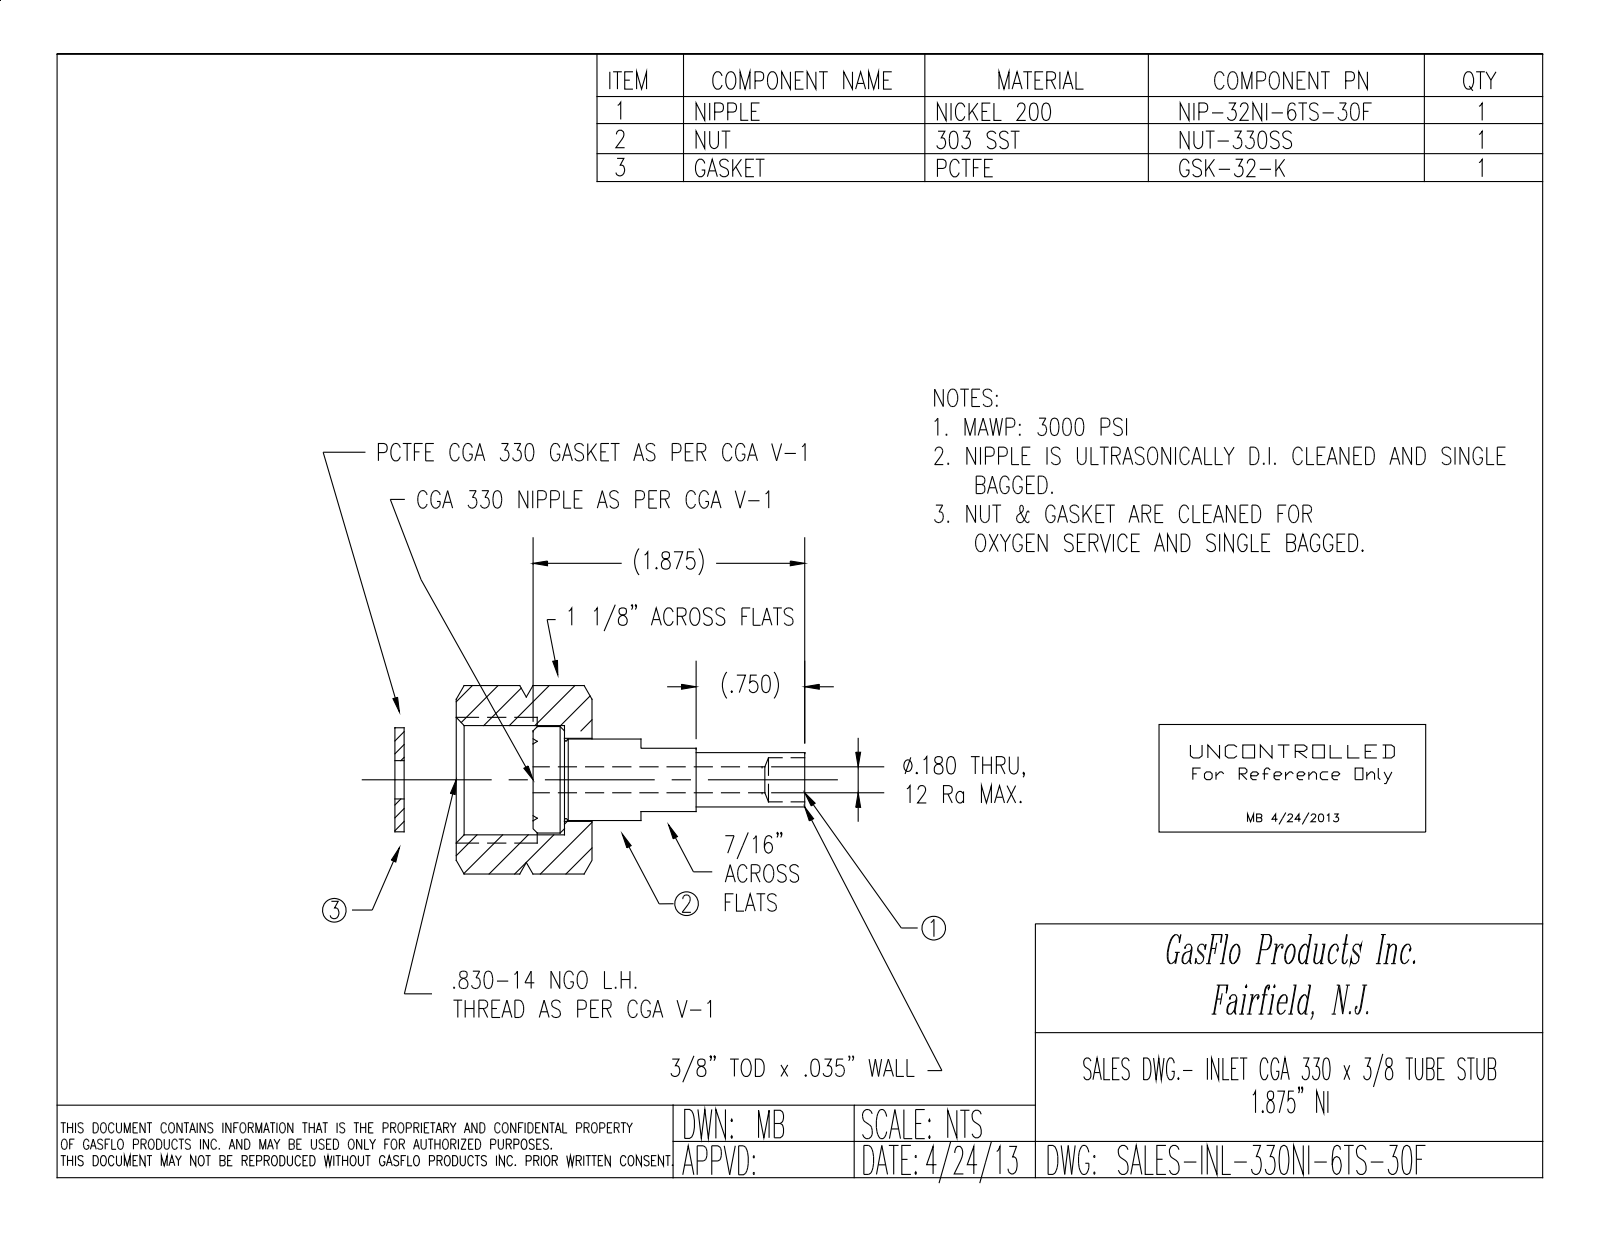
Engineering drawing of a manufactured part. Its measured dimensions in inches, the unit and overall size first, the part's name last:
Units: inches
Overall size (bounding box): 2.431 × 1.299 × 1.125
Round holes (diameter × count): ⌀0.18 ×1, ⌀0.25 ×1, ⌀0.304 ×1, ⌀0.57 ×1, ⌀0.757 ×1
Round bosses / shafts (diameter × count): ⌀0.736 ×1, ⌀0.703 ×1, ⌀0.56 ×1, ⌀0.377 ×1
Main face-to-face distances: 1.125, 0.194, 0.389, 1.125, 0.944, 0.556, 0.483, 0.094, 0.461, 0.289
Volume: 0.977 in³ · Surface area: 13.94 in²
Bodies: 3 solids, 191 faces (37 planar, 36 cylindrical, 118 other)
Part name (STEP PRODUCT): PRT-001503; INL-330NI-6TS-30F; PRT-000260; PRT-000034
STEP written by: SolidWorks 2018 (CONFIG_CONTROL_DESIGN)
